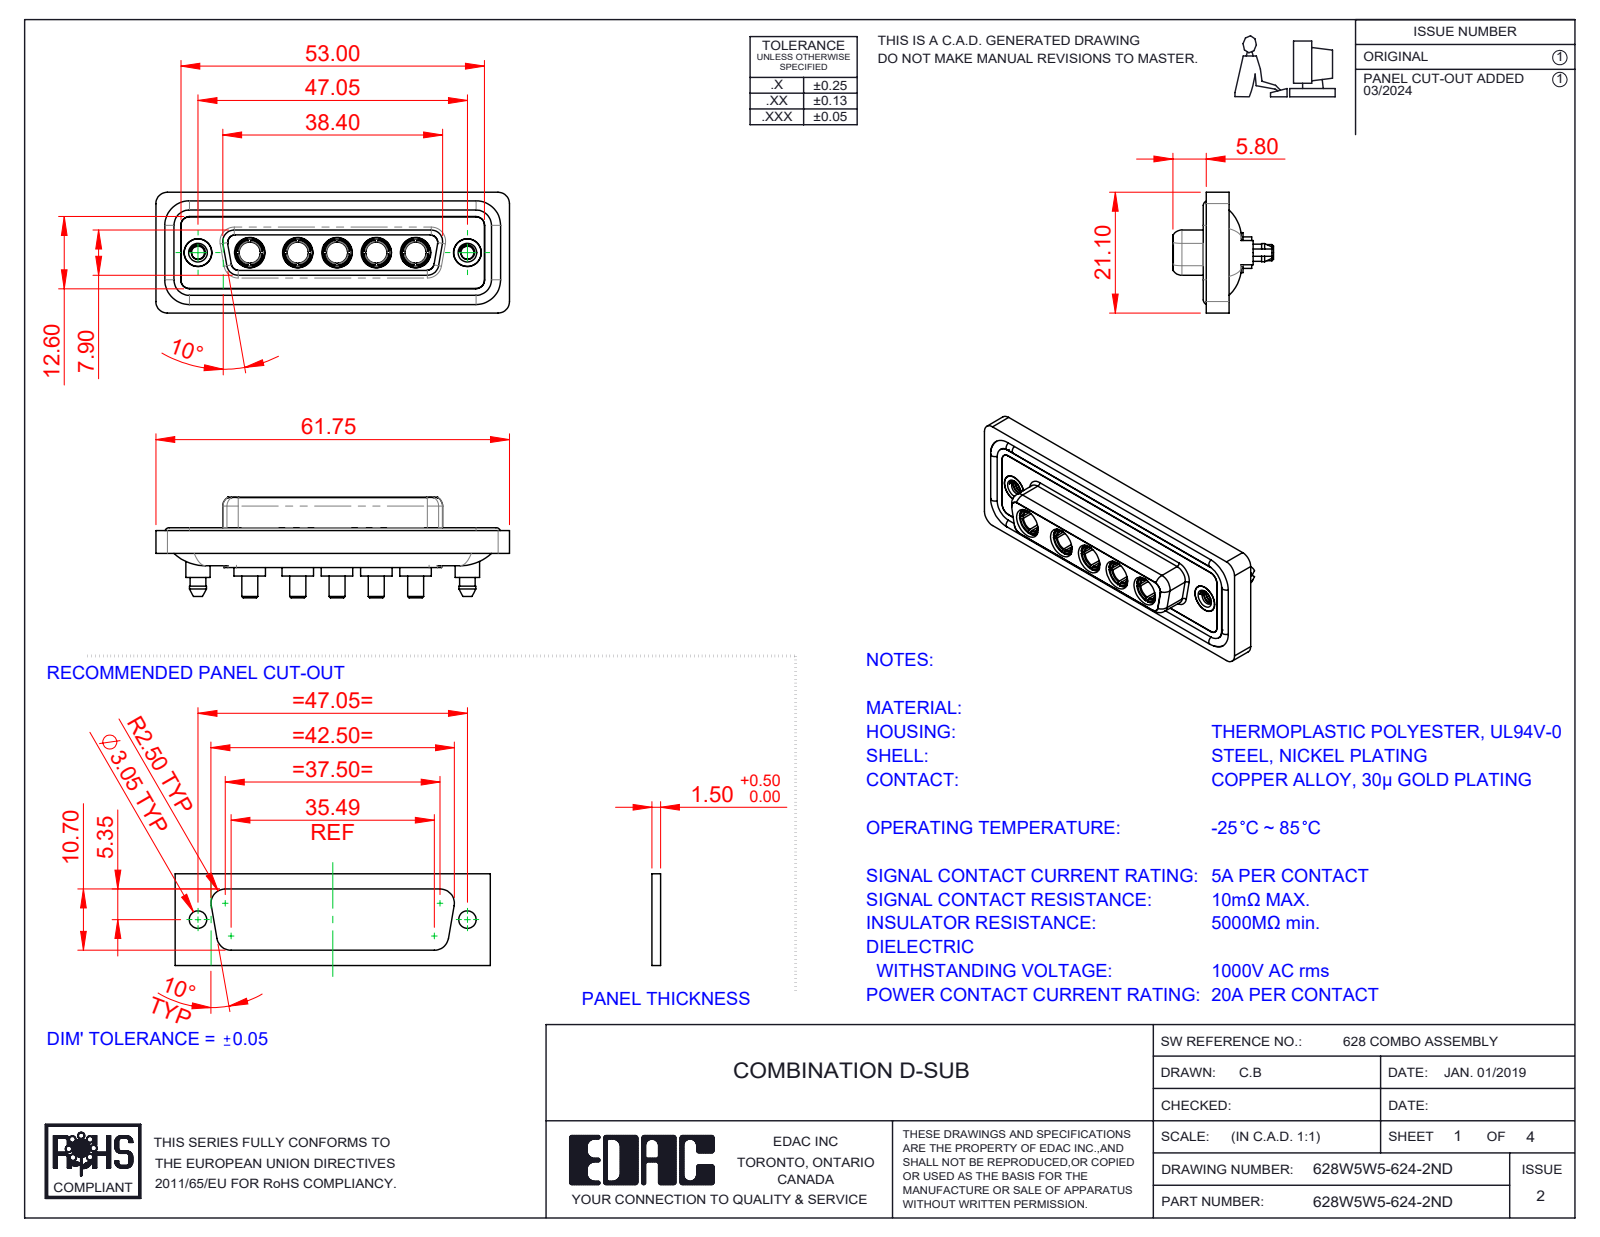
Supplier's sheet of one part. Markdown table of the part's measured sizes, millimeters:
| quantity | value |
| --- | --- |
| part name | 628Combo Housing_5W5; 628Combo Waterproof Housing_25 Contacts; 628W5W5-624-2ND; 628Combo Shell Front_25 Contacts (+3 more) |
| STEP written by | SolidWorks 2023 (CONFIG_CONTROL_DESIGN) |
| units | millimeters |
| bodies | 17 solids, 822 faces (266 planar, 351 cylindrical, 205 other) |
| overall size | 61.75 × 21.1 × 17.55 |
| volume | 8 308 mm³ |
| surface area | 13 755 mm² |
| round holes (diameter × count) | 4.85 × 7, 3.7 × 5, 5.3 × 5, 2.26 × 2, 4 × 2, 4.05 × 2, 5 × 2 |
| round bosses / shafts (diameter × count) | 5.5 × 5, 5.2 × 5, 4.96 × 5, 4.75 × 5, 3.75 × 5, 2.8 × 5, 1.6 × 4, 5.4 × 2 |
| partial cylindrical surfaces (radius × count) | 1.5 × 24, 2 × 18, 1.6 × 10, 1.35 × 8, 2.1 × 5, 0.25 × 4, 0.5 × 4, 0.6 × 4 |
| main face-to-face distances | 0.4, 1.8, 7.45, 5.65, 0.5, 7.05, 6.6, 1.6, 1.1, 2.9 |
| hole center spacings | 6.86, 9.04, 13.72, 38.01, 8.39, 15.25, 15.9, 17.43 |
